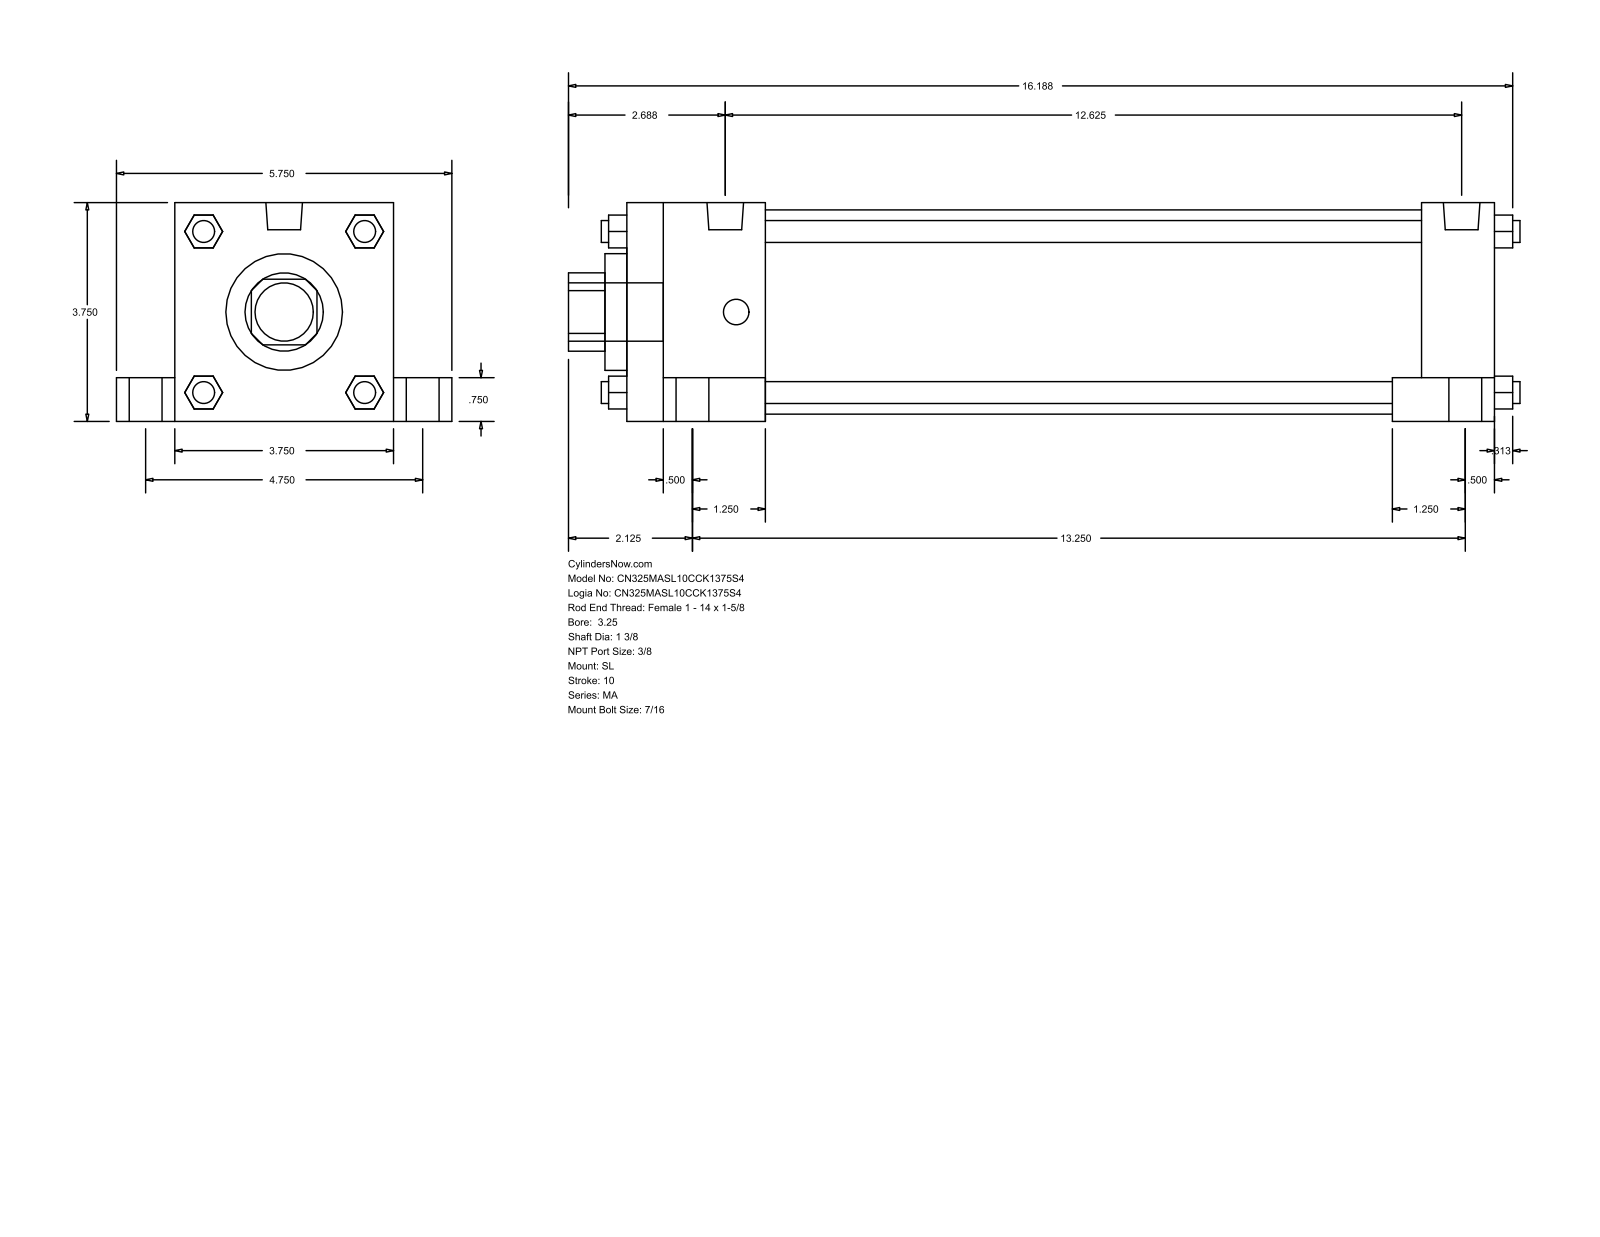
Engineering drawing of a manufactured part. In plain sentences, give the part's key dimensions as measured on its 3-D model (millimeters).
The part is named "MA_SL__0325_1.375". Its 3-D file was written by "GSSL Pune (CONFIG_CONTROL_DESIGN)". It is 0 solids with 148 faces: 112 planar, 36 cylindrical and 0 other. Overall it measures 414.34 by 146.05 by 95.25 millimeters. Round holes: 1 of diameter 34.92, 1 of diameter 50.8, 1 of diameter 88.9. Round bosses or shafts: 4 of diameter 20.64, 4 of diameter 14.29, 4 of diameter 11.11, 4 of diameter 9.53, 2 of diameter 15.93, 1 of diameter 25.4. Partial cylindrical surfaces (rounded edges, fillets, slot ends): 1 of radius 17.06. The main face-to-face distances are 95.24, 377.83, 25.41, 120.65, 346.08, 31.75, 60.32, 285.76, 317.51, 19.05.
